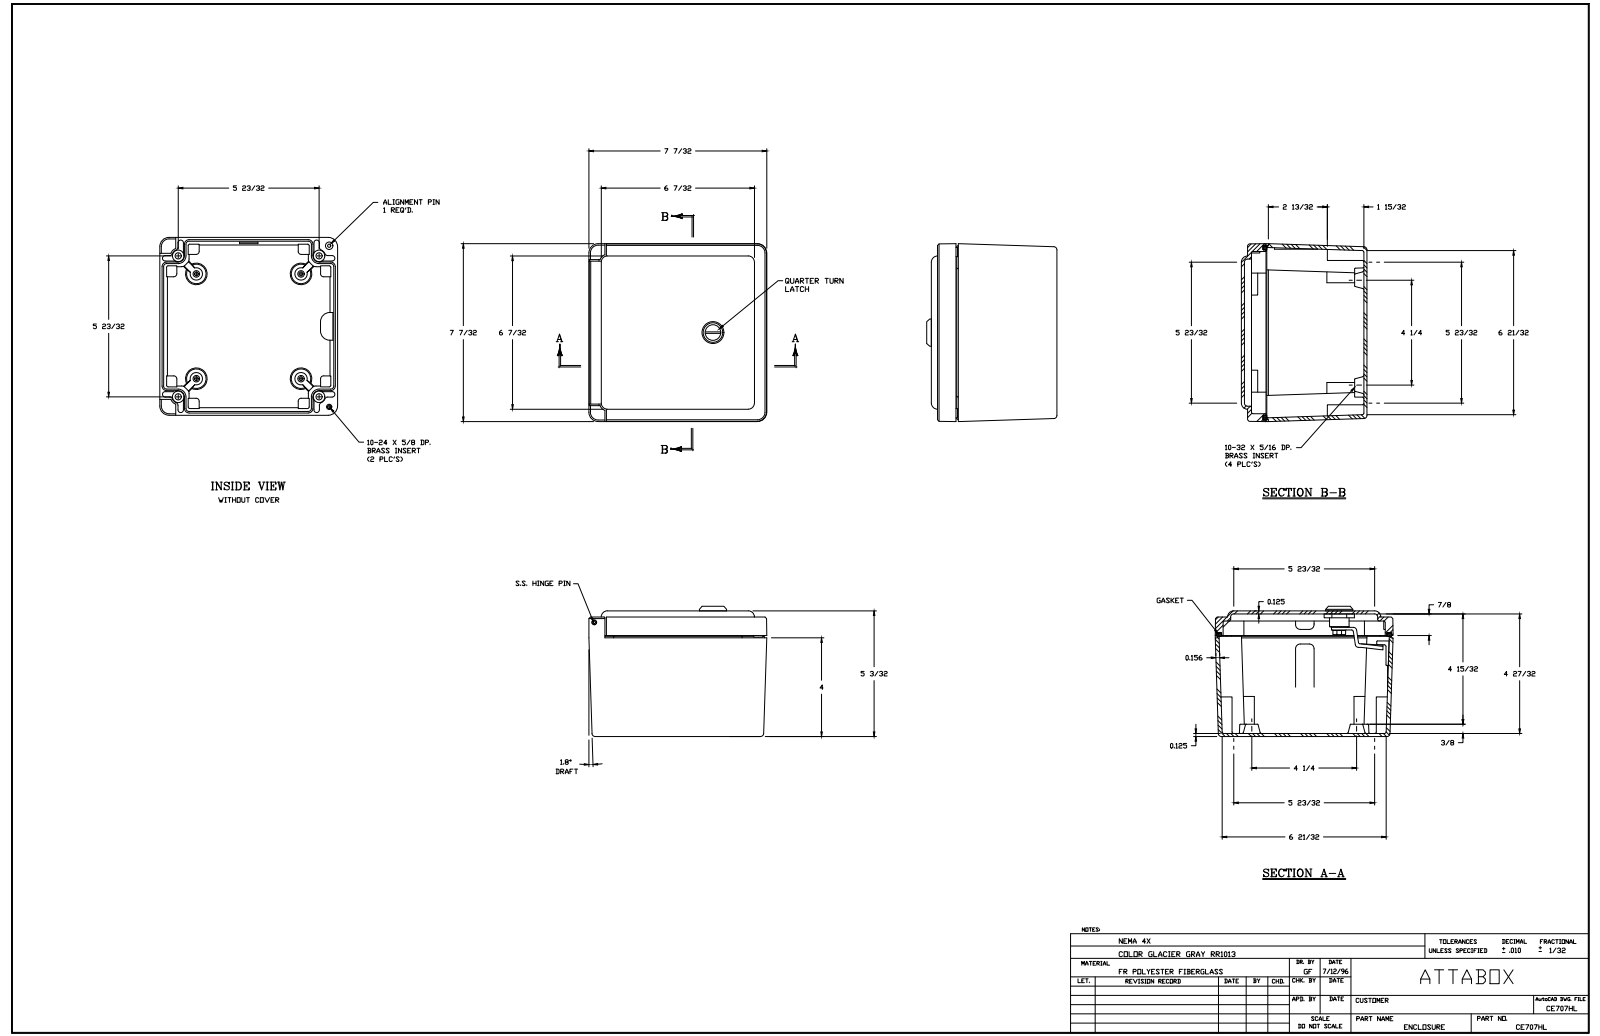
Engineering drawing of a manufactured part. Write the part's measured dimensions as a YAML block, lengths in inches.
part_name: "CE707HL"
step_written_by: "SolidWorks 2018 (AUTOMOTIVE_DESIGN)"
units: inches
bodies: {solids: 34, faces: 1738, planar: 755, cylindrical: 510, other: 473}
overall_size: [9.783, 7.273, 5.501]
volume: 55.13
surface_area: 619.1
round_holes:
  - {diameter: 0.159, count: 6}
  - {diameter: 0.281, count: 6}
  - {diameter: 0.313, count: 4}
  - {diameter: 0.313, count: 4}
  - {diameter: 0.344, count: 4}
  - {diameter: 0.531, count: 4}
  - {diameter: 0.096, count: 2}
  - {diameter: 0.156, count: 2}
  - {diameter: 0.219, count: 2}
  - {diameter: 0.23, count: 2}
  - {diameter: 0.28, count: 2}
  - {diameter: 0.114, count: 1}
round_bosses_or_shafts:
  - {diameter: 0.27, count: 6}
  - {diameter: 0.229, count: 4}
  - {diameter: 0.375, count: 2}
  - {diameter: 1.102, count: 1}
  - {diameter: 0.866, count: 1}
  - {diameter: 0.78, count: 1}
  - {diameter: 0.622, count: 1}
  - {diameter: 0.598, count: 1}
partial_cylinders:
  - {radius: 0.031, count: 56}
  - {radius: 0.031, count: 50}
  - {radius: 0.125, count: 36}
  - {radius: 0.012, count: 31}
  - {radius: 0.062, count: 17}
  - {radius: 0.02, count: 12}
  - {radius: 0.063, count: 12}
  - {radius: 0.1, count: 12}
face_to_face_distances: [0.125, 4.969, 5.094, 0.186, 0.186, 4.844, 0.25, 0.125, 5.219, 0.75]
hole_center_spacings: [8.09, 1.039, 1.375, 2.239, 5.039, 5.04, 5.426, 5.896]
